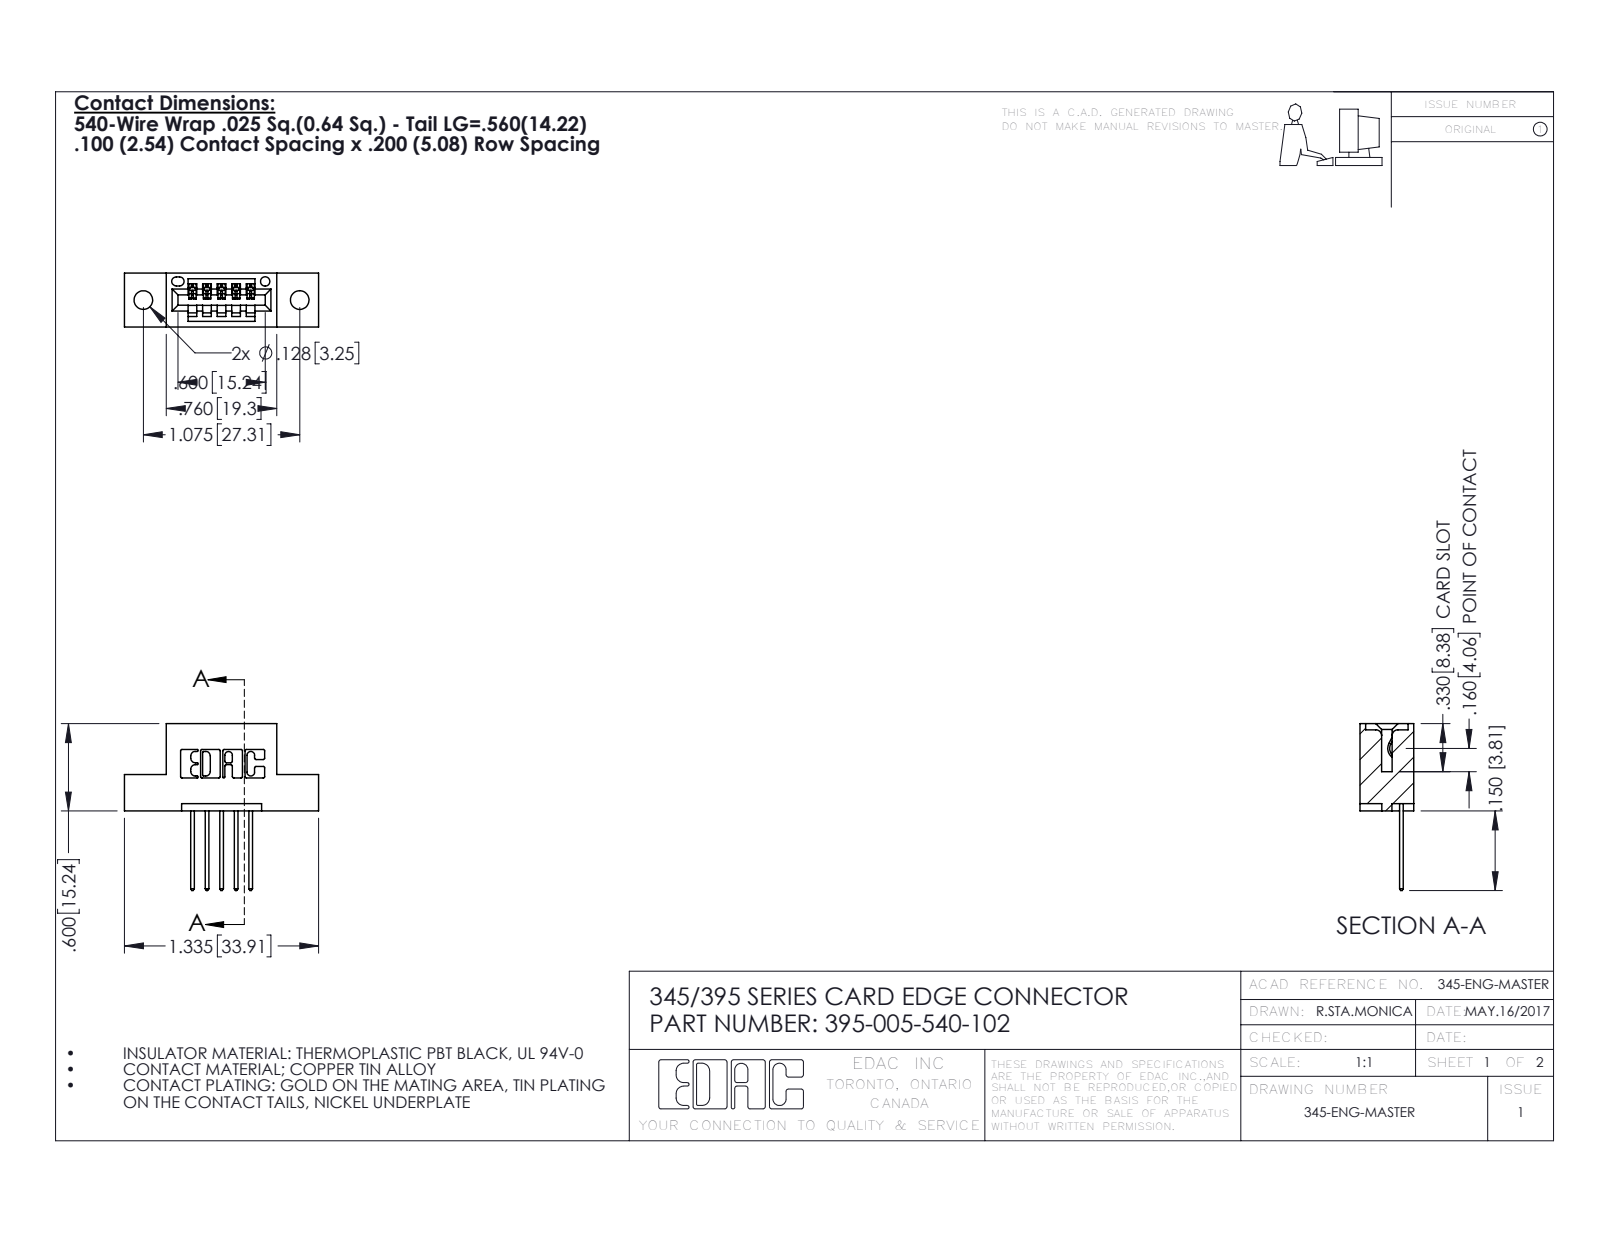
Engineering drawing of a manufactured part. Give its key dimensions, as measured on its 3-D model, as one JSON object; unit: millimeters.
{"part_name": "345 Part_Flush Mounting Lugs - 0.128 Dia; 395-005-540-102; 345-292-001_345-293-140", "step_written_by": "SolidWorks 2016 (CONFIG_CONTROL_DESIGN)", "units": "millimeters", "bodies": {"solids": 6, "faces": 416, "planar": 280, "cylindrical": 136, "other": 0}, "overall_size": [33.9, 29.1, 9.4], "volume_mm3": 2880, "surface_area_mm2": 3112, "round_holes": [[3.3, 2], [1.6, 1]], "partial_cylinders_radius": [[0.3, 22], [0.2, 10], [0.3, 10], [0.2, 6], [0.8, 6], [0.7, 3], [0.8, 2], [1, 2]], "face_to_face_distances": [5.1, 9.4, 7.6, 1.8, 2.5, 0.6, 2.5, 6.9, 6.4, 1.5], "hole_center_spacings": [6.9, 21.5, 27.3]}
